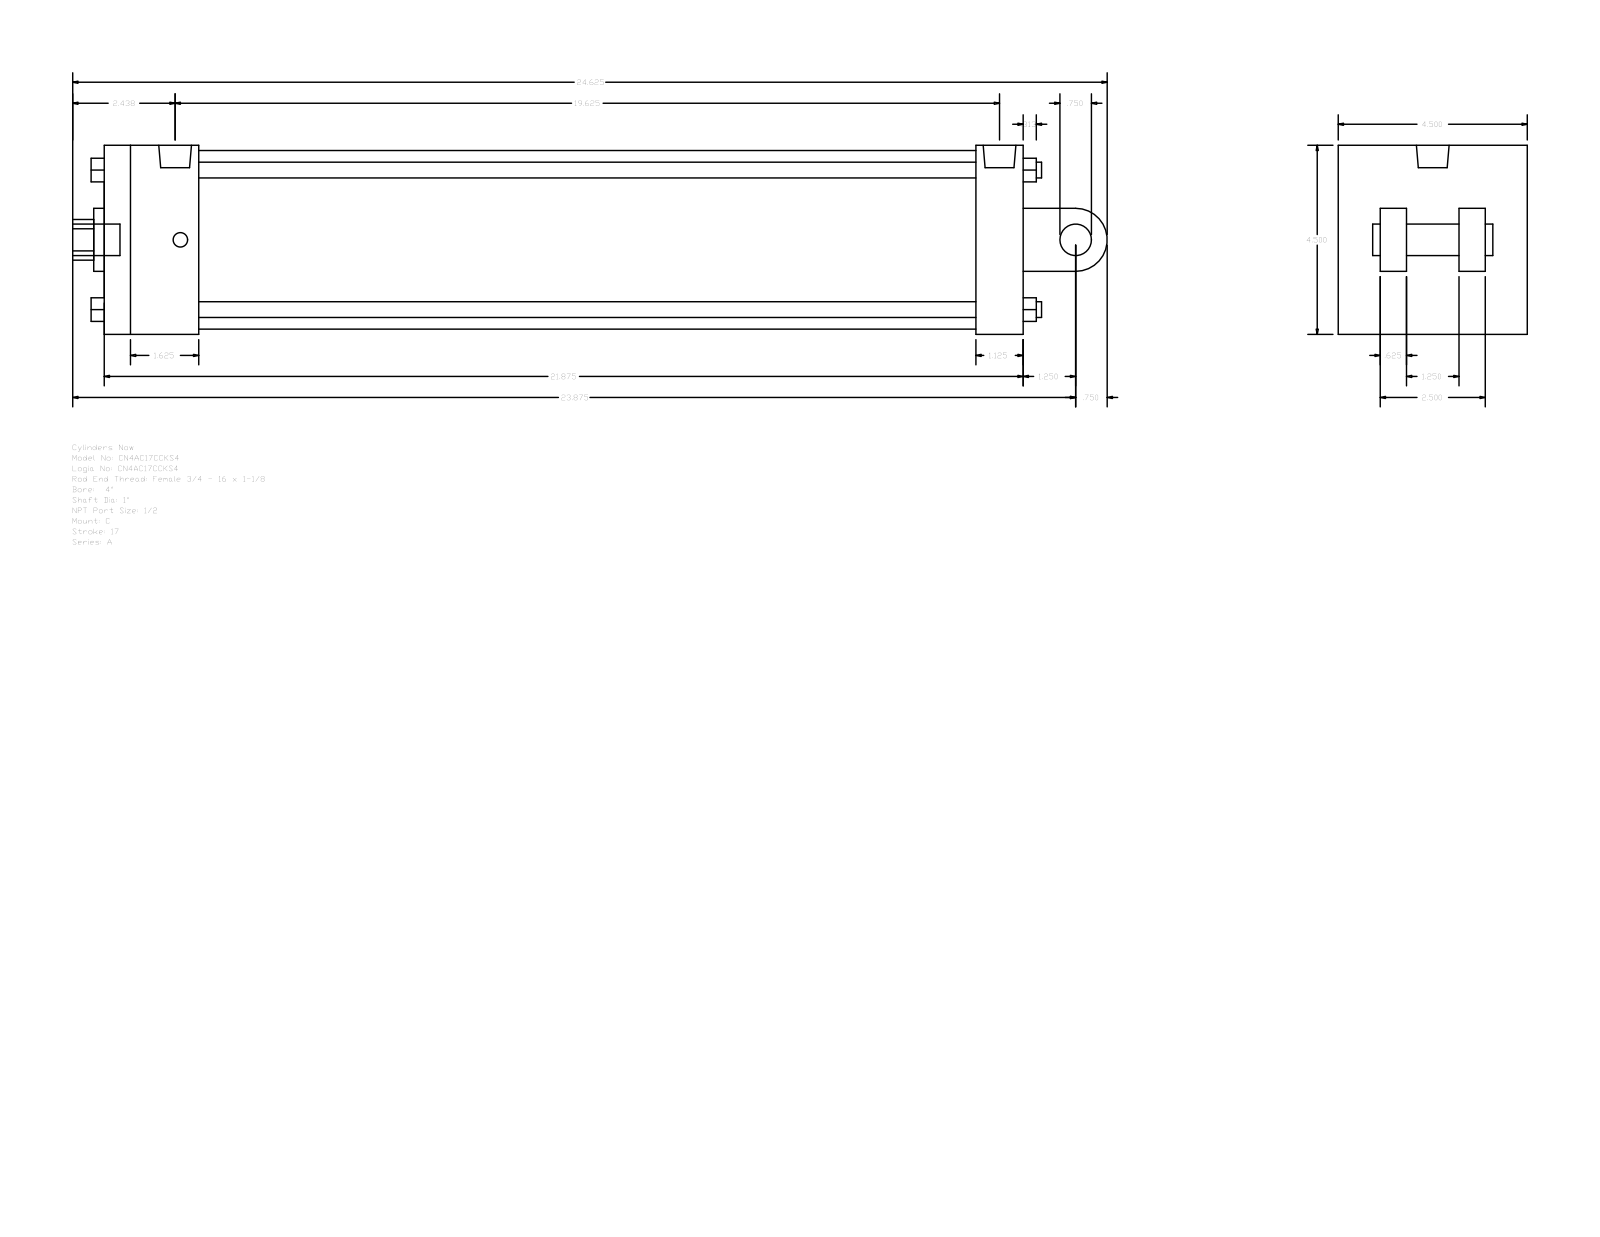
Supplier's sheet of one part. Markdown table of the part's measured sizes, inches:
| quantity | value |
| --- | --- |
| part name | A_C__0400_1 |
| STEP written by | GSSL Pune (CONFIG_CONTROL_DESIGN) |
| units | inches |
| bodies | 0 solids, 135 faces (102 planar, 33 cylindrical, 0 other) |
| overall size | 24.625 × 4.5 × 4.5 |
| round holes (diameter × count) | 0.344 × 2, 0.778 × 1, 1 × 1, 1.5 × 1, 4.25 × 1 |
| round bosses / shafts (diameter × count) | 0.375 × 4, 0.75 × 2, 0.344 × 2, 0.778 × 1 |
| partial cylindrical surfaces (radius × count) | 0.484 × 1, 0.75 × 1 |
| main face-to-face distances | 4.5, 21.875, 2.875, 1.125, 20.75, 2.25, 18.5, 19.625, 0.625, 1.875 |
| hole center spacings | 0.125 |
